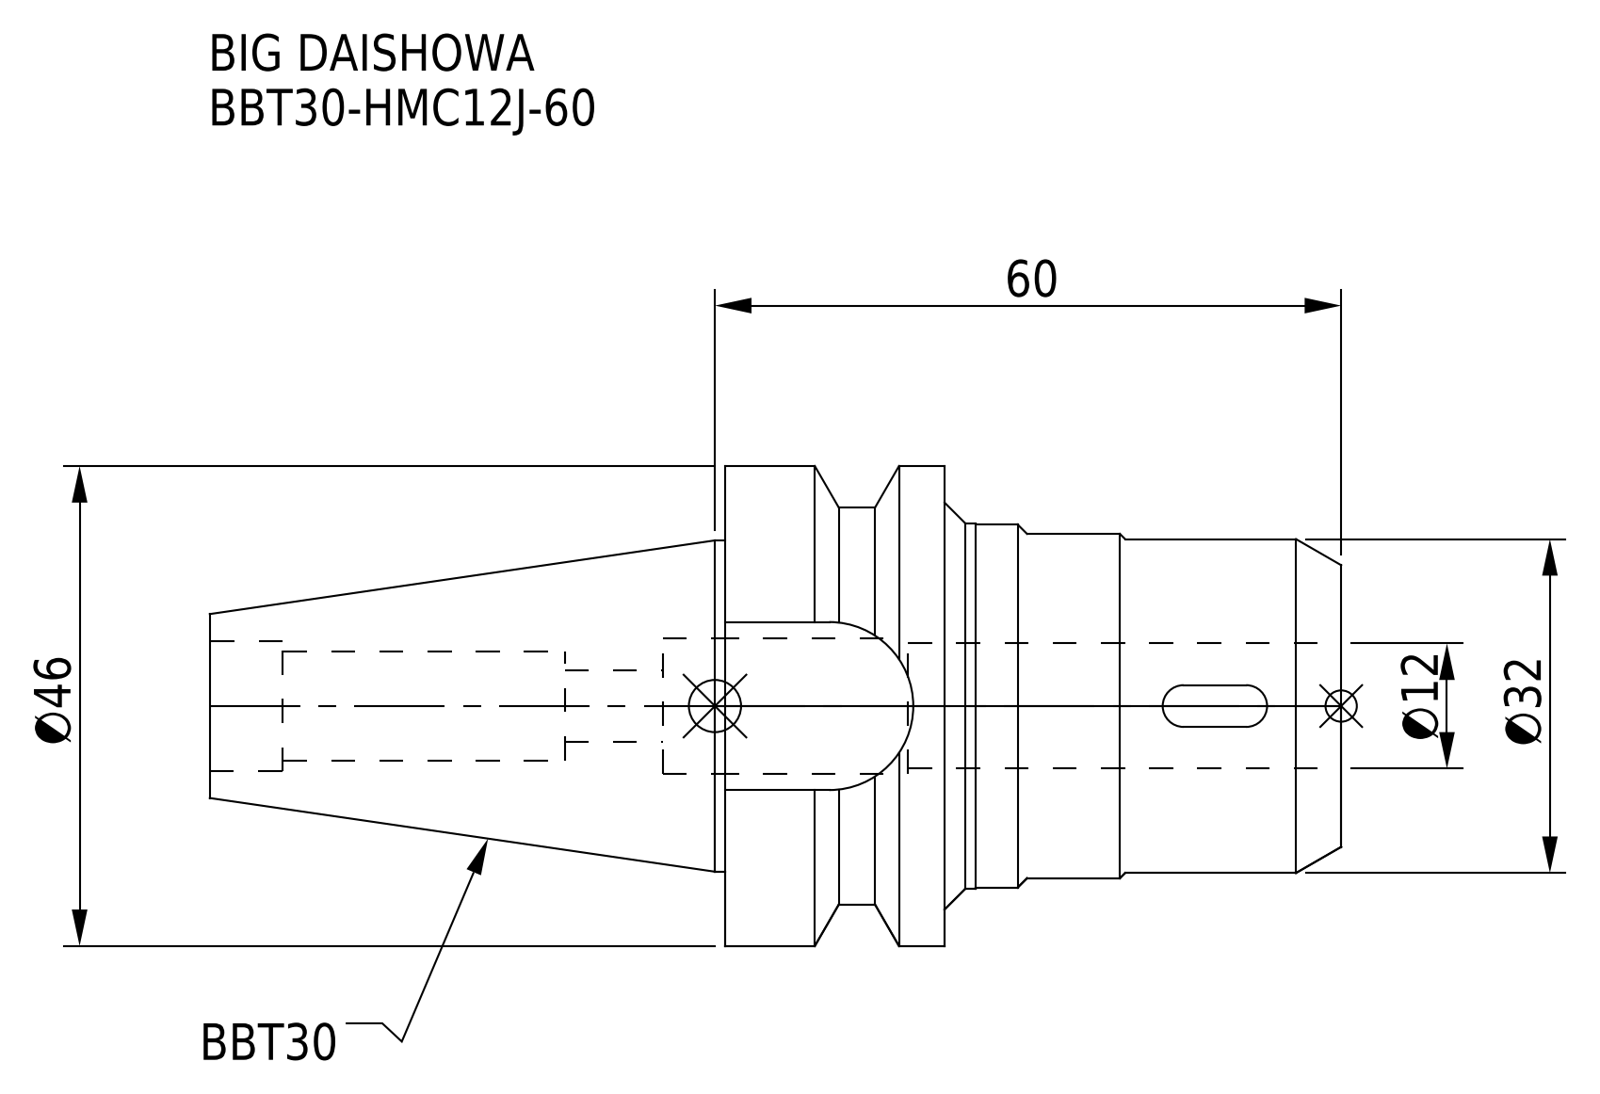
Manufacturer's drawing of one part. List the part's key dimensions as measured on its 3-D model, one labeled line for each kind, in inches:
Part name (STEP PRODUCT): BBT30-HMC12J-60
STEP written by: CREO PARAMETRIC BY PTC INC, 2016380 (AUTOMOTIVE_DESIGN)
Units: inches
Bodies: 1 solid, 79 faces (27 planar, 38 cylindrical, 14 other)
Overall size (bounding box): 4.268 × 1.811 × 1.811
Volume: 4.528 in³ · Surface area: 27.47 in²
Round holes (diameter × count): ⌀0.268 ×1, ⌀0.409 ×1, ⌀0.472 ×1, ⌀0.492 ×1, ⌀0.512 ×1
Round bosses / shafts (diameter × count): ⌀1.811 ×1, ⌀1.378 ×1, ⌀1.37 ×1, ⌀1.299 ×1, ⌀1.26 ×1, ⌀1.25 ×1
Partial cylindrical surfaces — rounded edges, fillets, slot ends (radius × count): R0.079 ×4, R0.317 ×1, R0.748 ×1
Main face-to-face distances: 0.827, 1.496, 2.323, 1.283, 1.063, 4.268, 2.772, 1.945, 0.634, 2.559
